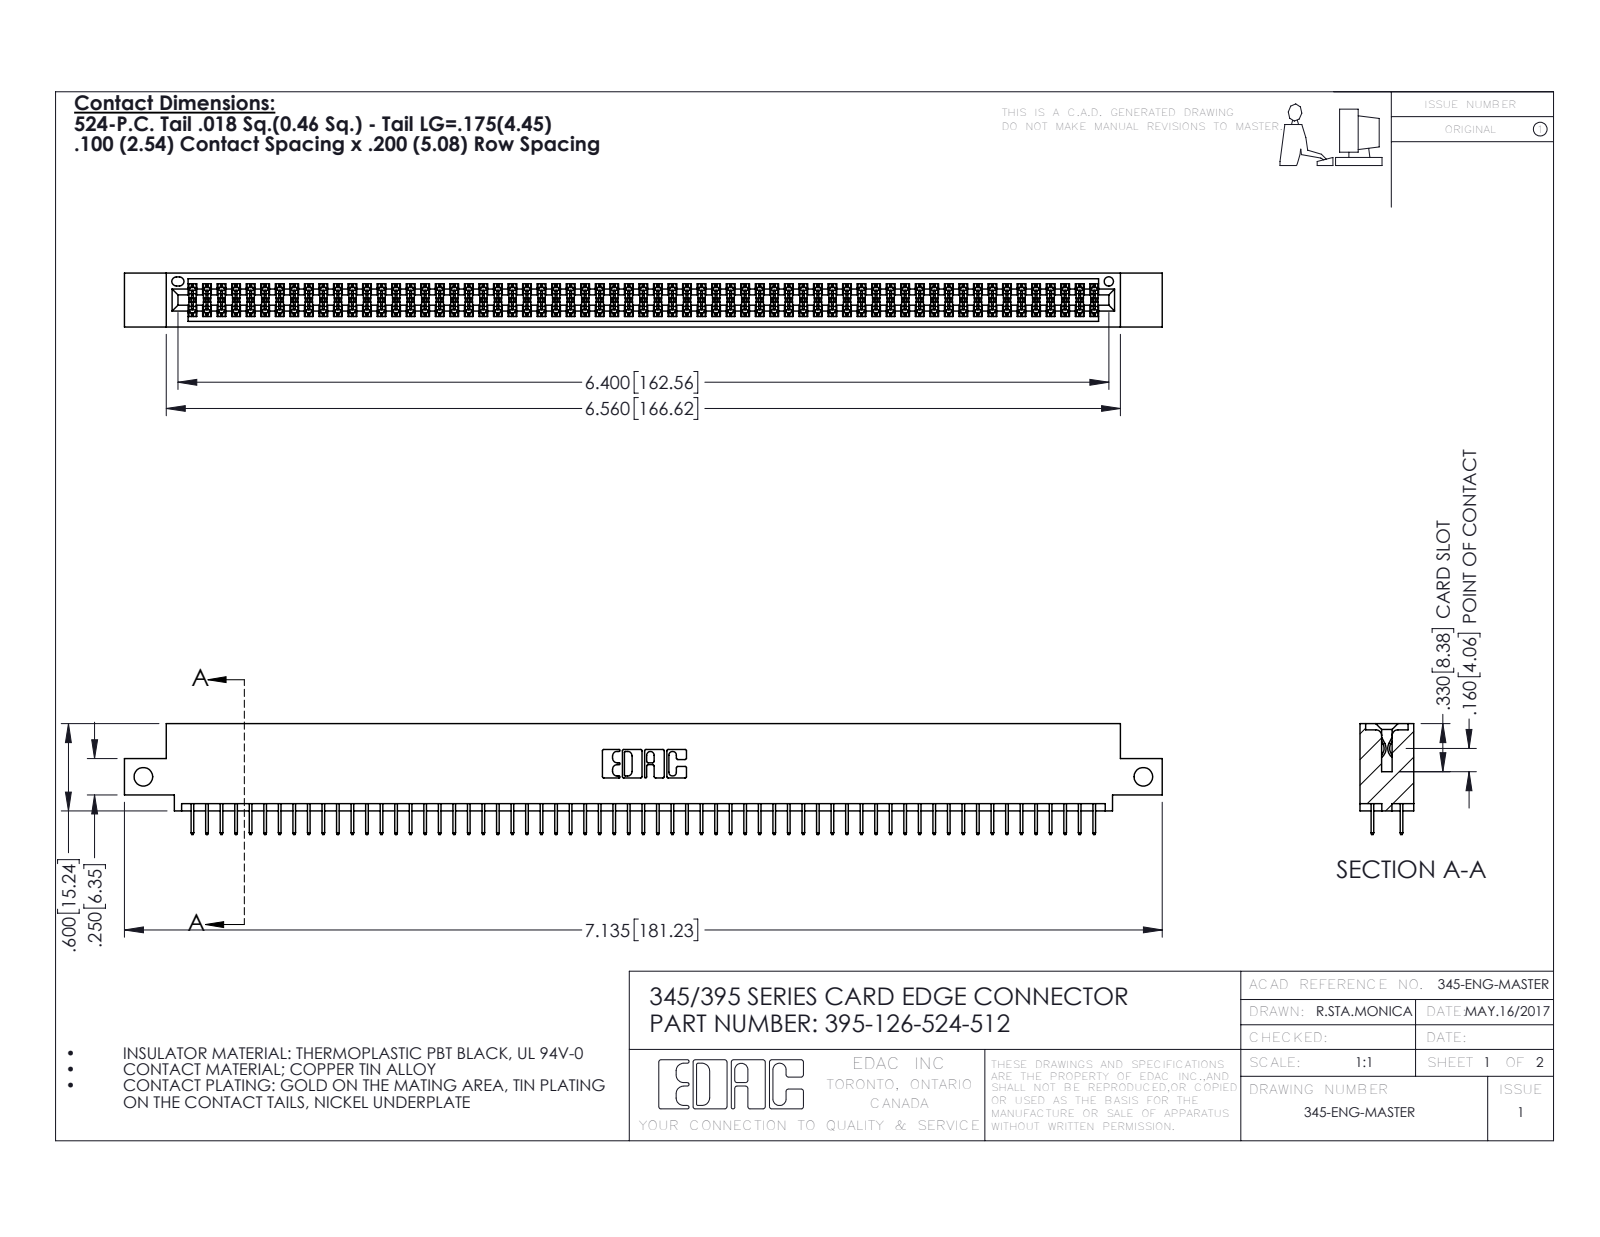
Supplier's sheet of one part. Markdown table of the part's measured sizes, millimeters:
| quantity | value |
| --- | --- |
| part name | 345-292-001_345-293-124; 345 Part_0.110 Offset - Side Mount; 395-126-524-512 |
| STEP written by | SolidWorks 2016 (CONFIG_CONTROL_DESIGN) |
| units | millimeters |
| bodies | 127 solids, 6934 faces (4998 planar, 1936 cylindrical, 0 other) |
| overall size | 181.2 × 19.4 × 9.4 |
| volume | 17 450 mm³ |
| surface area | 25 650 mm² |
| round holes (diameter × count) | 3.3 × 2, 1.6 × 1 |
| partial cylindrical surfaces (radius × count) | 0.2 × 189, 0.3 × 22, 0.2 × 6, 0.8 × 6, 0.7 × 3, 0.4 × 2, 0.5 × 2, 0.6 × 2 |
| main face-to-face distances | 1.8, 7.6, 5.1, 9.4, 2.5, 6.9, 0.6, 5.7, 1.8, 4.4 |
| hole center spacings | 174.6 |
